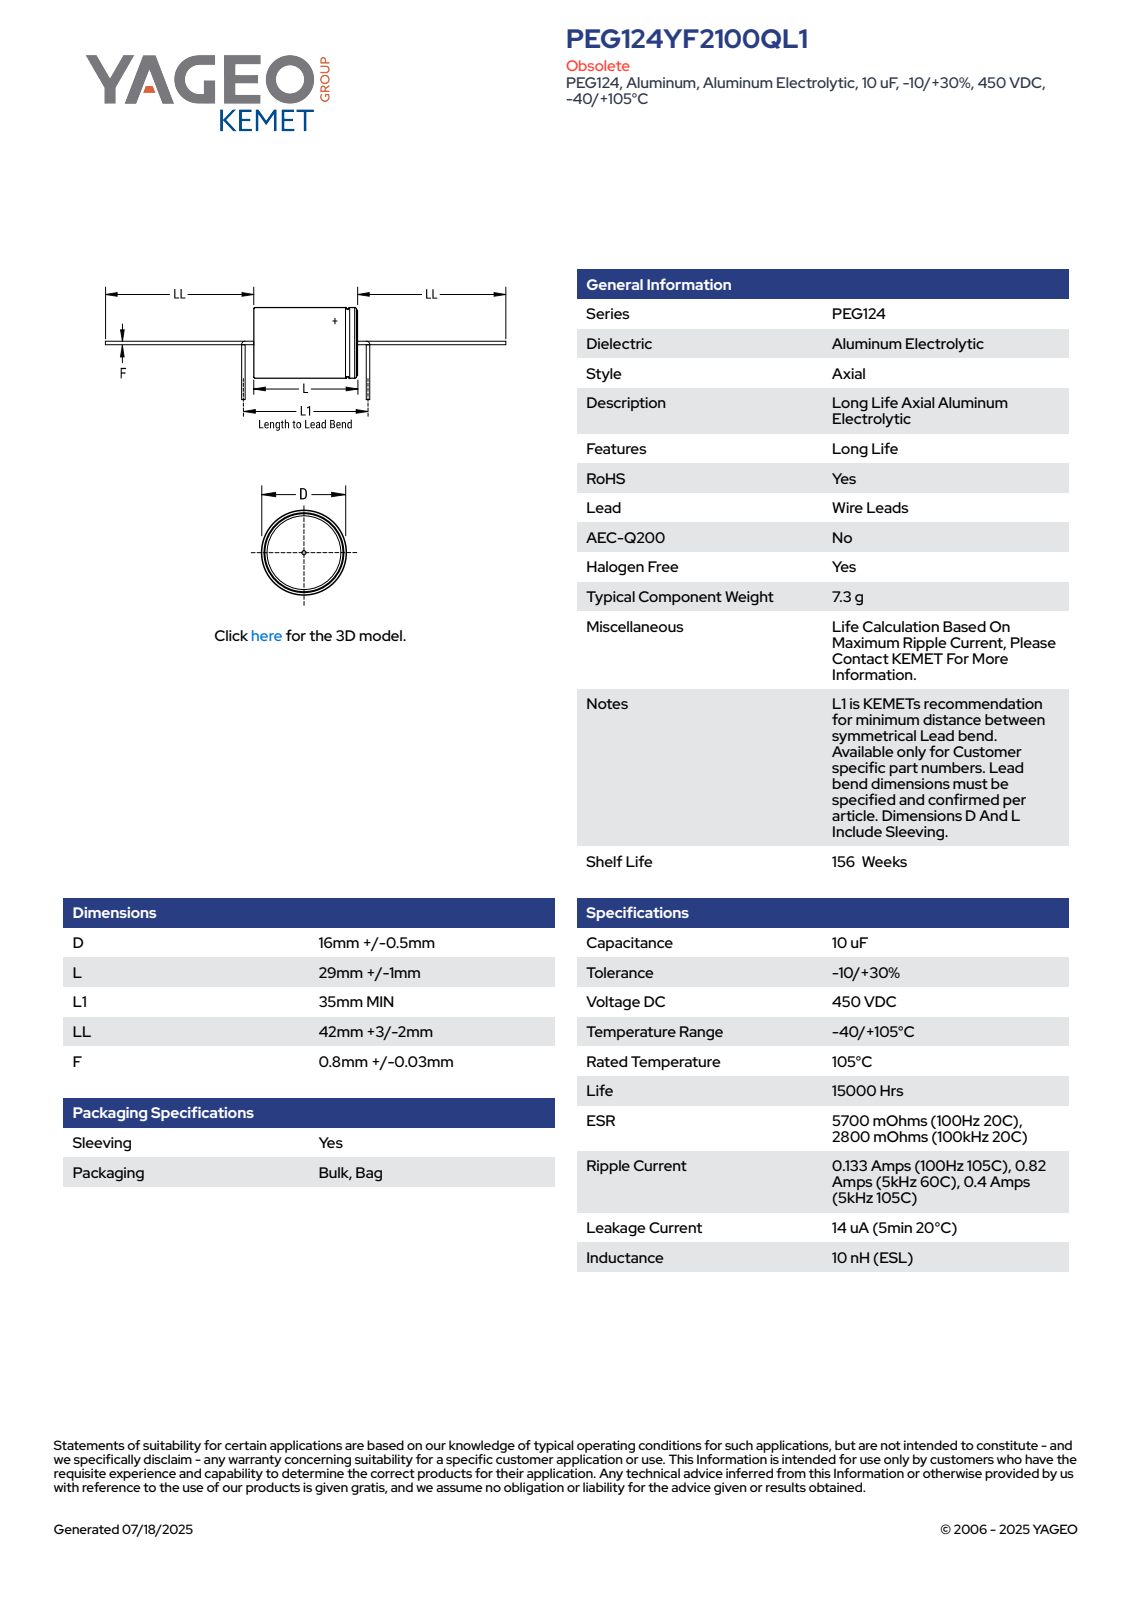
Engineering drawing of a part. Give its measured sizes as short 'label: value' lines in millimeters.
name: CAA_PEG124_16X29_D16.5L30LL45F0.83
written by: SolidWorks 2014 (AUTOMOTIVE_DESIGN)
unit: mm
bodies: 1 solid, 99 faces (27 planar, 29 cylindrical, 43 other)
size: 117 × 16.5 × 16.5
volume: 6 266 mm³; area: 2 264 mm²
holes: 1× ⌀15.5
bosses: 1× ⌀16.5, 1× ⌀16, 1× ⌀0.83
rounds: 1× R8.24
face distances: 29, 30, 1, 45, 74, 75, 117, 72, 43, 42
